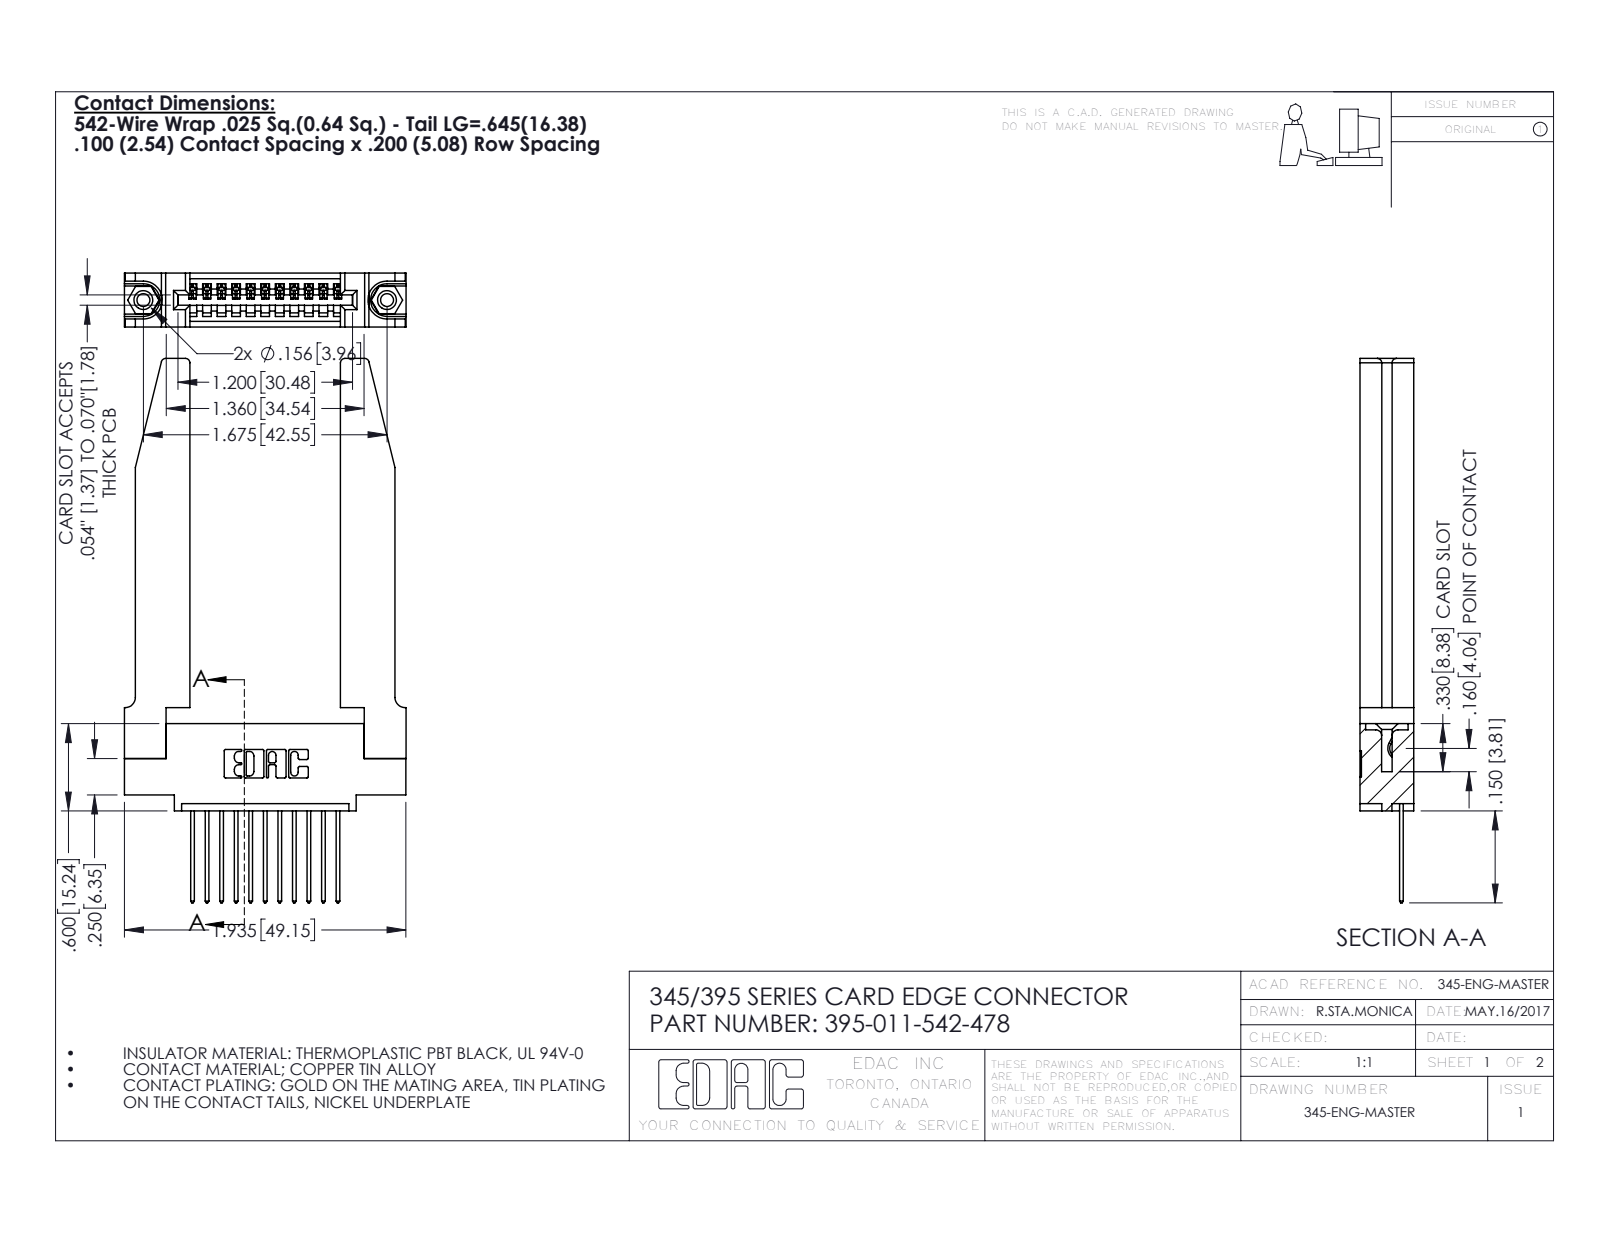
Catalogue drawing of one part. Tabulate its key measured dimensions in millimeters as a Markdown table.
| quantity | value |
| --- | --- |
| part name | 345 Part_0.110 Offset - 0.156 Dia-TH; 345-220-078_345-220-078; 345-292-001_345-293-142; 395-011-542-478 (+1 more) |
| STEP written by | SolidWorks 2016 (CONFIG_CONTROL_DESIGN) |
| units | millimeters |
| bodies | 16 solids, 1002 faces (666 planar, 284 cylindrical, 52 other) |
| overall size | 95 × 49.2 × 9.4 |
| volume | 12 100 mm³ |
| surface area | 12 460 mm² |
| round holes (diameter × count) | 2.3 × 2, 3.2 × 2, 4 × 2, 1.6 × 1 |
| round bosses / shafts (diameter × count) | 3.9 × 2 |
| partial cylindrical surfaces (radius × count) | 0.2 × 22, 0.3 × 22, 0.3 × 22, 0.8 × 8, 0.2 × 6, 0.8 × 6, 0.7 × 3, 0.8 × 2 |
| main face-to-face distances | 9.4, 1.8, 7.6, 3.8, 3.8, 5.6, 2, 26.3, 2.5, 6.9 |
| hole center spacings | 6.9, 36.7, 42.5 |
